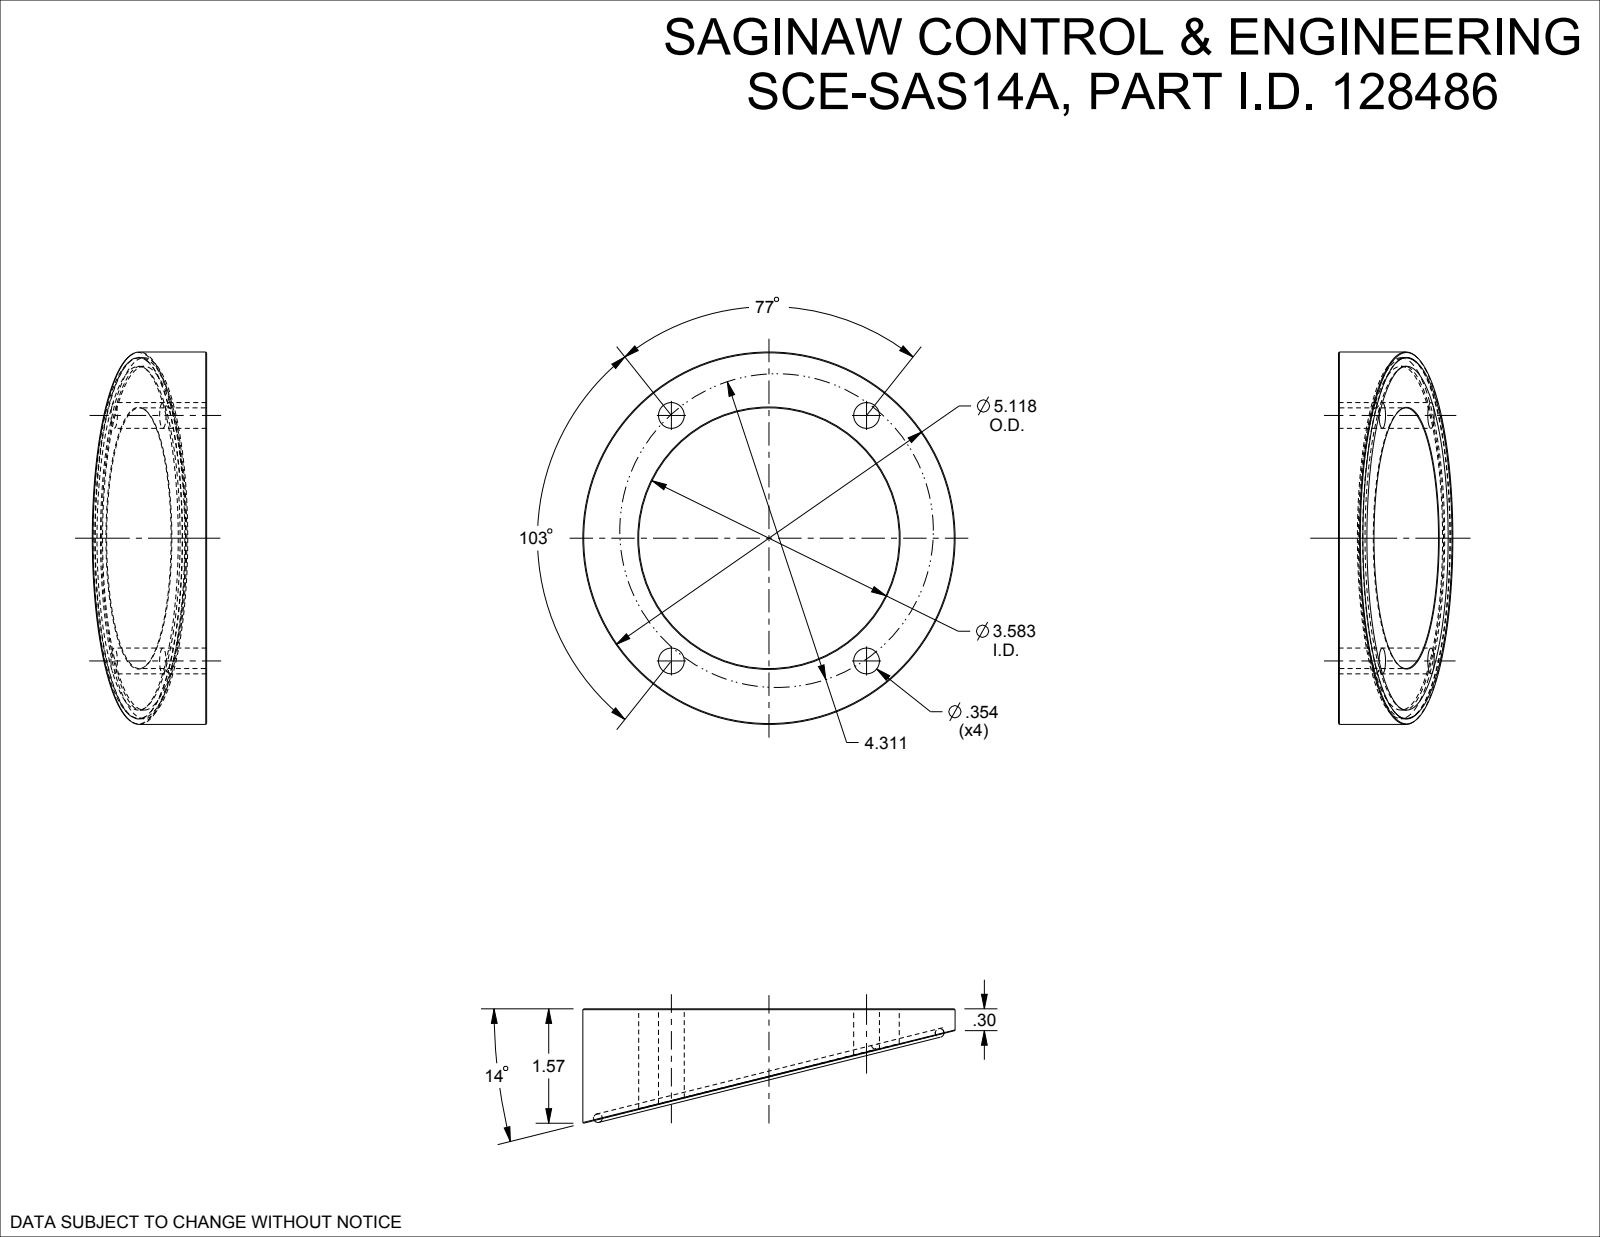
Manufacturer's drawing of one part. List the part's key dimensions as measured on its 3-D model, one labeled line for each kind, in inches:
Part name (STEP PRODUCT): SCE-SAS14A
STEP written by: SolidWorks 2023 (AUTOMOTIVE_DESIGN)
Units: inches
Bodies: 14 solids, 172 faces (116 planar, 36 cylindrical, 20 other)
Overall size (bounding box): 5.118 × 5.118 × 2.48
Volume: 10.85 in³ · Surface area: 83.86 in²
Round holes (diameter × count): ⌀0.354 ×8, ⌀3.583 ×1, ⌀4.961 ×1
Round bosses / shafts (diameter × count): ⌀0.512 ×4, ⌀0.315 ×4, ⌀0.307 ×4, ⌀5.118 ×1, ⌀4.724 ×1
Partial cylindrical surfaces — rounded edges, fillets, slot ends (radius × count): R0.047 ×6
Main face-to-face distances: 0.078, 0.669, 0.906, 1.575, 0.866, 0.289, 0.29, 0.098, 0.315, 3.374
Hole centre spacings: 2.156, 3.374, 2.683, 4.311, 2.751, 4.353
